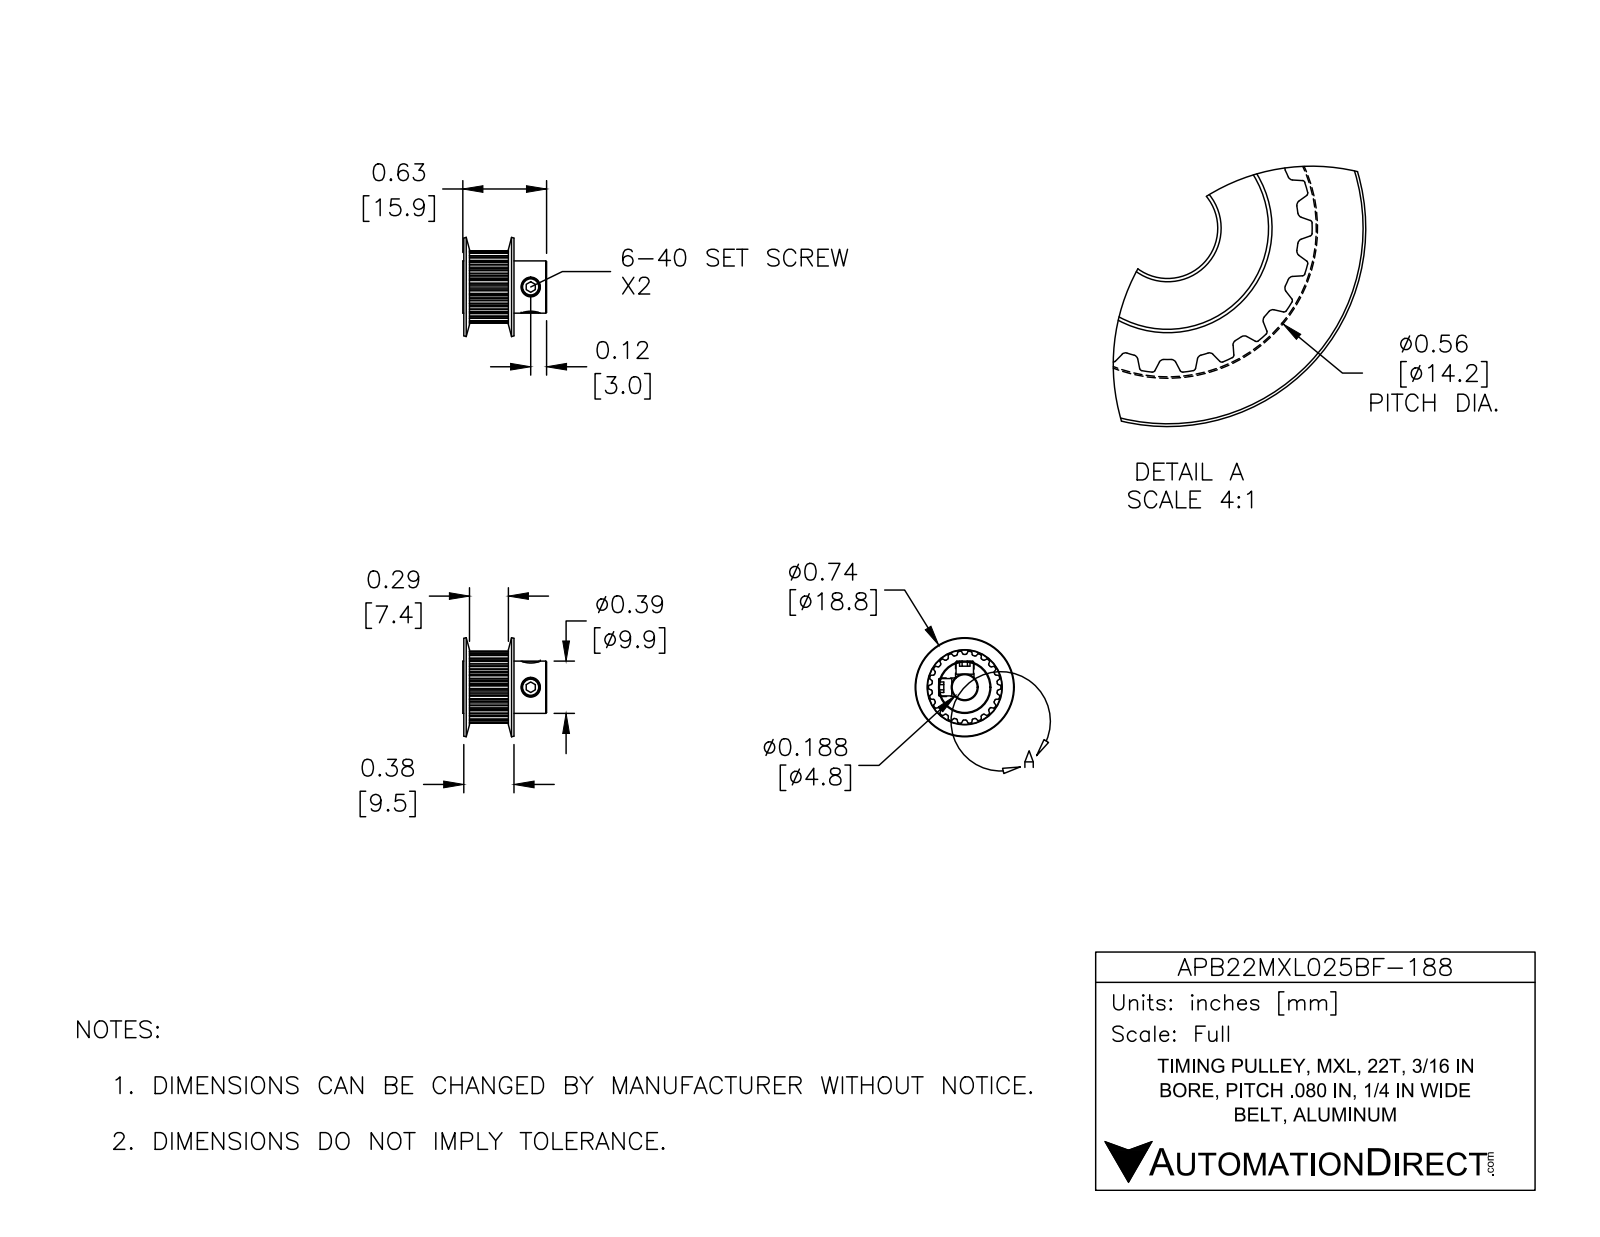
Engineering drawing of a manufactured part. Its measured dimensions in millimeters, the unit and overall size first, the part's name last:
Units: millimetres
Overall size (bounding box): 18.8 × 18.8 × 15.9
Round holes (diameter × count): ⌀3.5 ×2, ⌀4.7 ×1
Round bosses / shafts (diameter × count): ⌀3.3 ×2, ⌀9.9 ×1
Partial cylindrical surfaces — rounded edges, fillets, slot ends (radius × count): R0.1 ×44, R0.2 ×44, R6.2 ×1, R6.9 ×1
Main face-to-face distances: 8.6, 5.3, 0.6, 9.2, 15.9, 15.2, 6.6, 8.6, 8, 0.6
Volume: 1 600 mm³ · Surface area: 1 852 mm²
Bodies: 3 solids, 257 faces (68 planar, 163 cylindrical, 26 other)
Part name (STEP PRODUCT): APB22MXL025BF-188
STEP written by: SolidWorks 2016 (AUTOMOTIVE_DESIGN)
